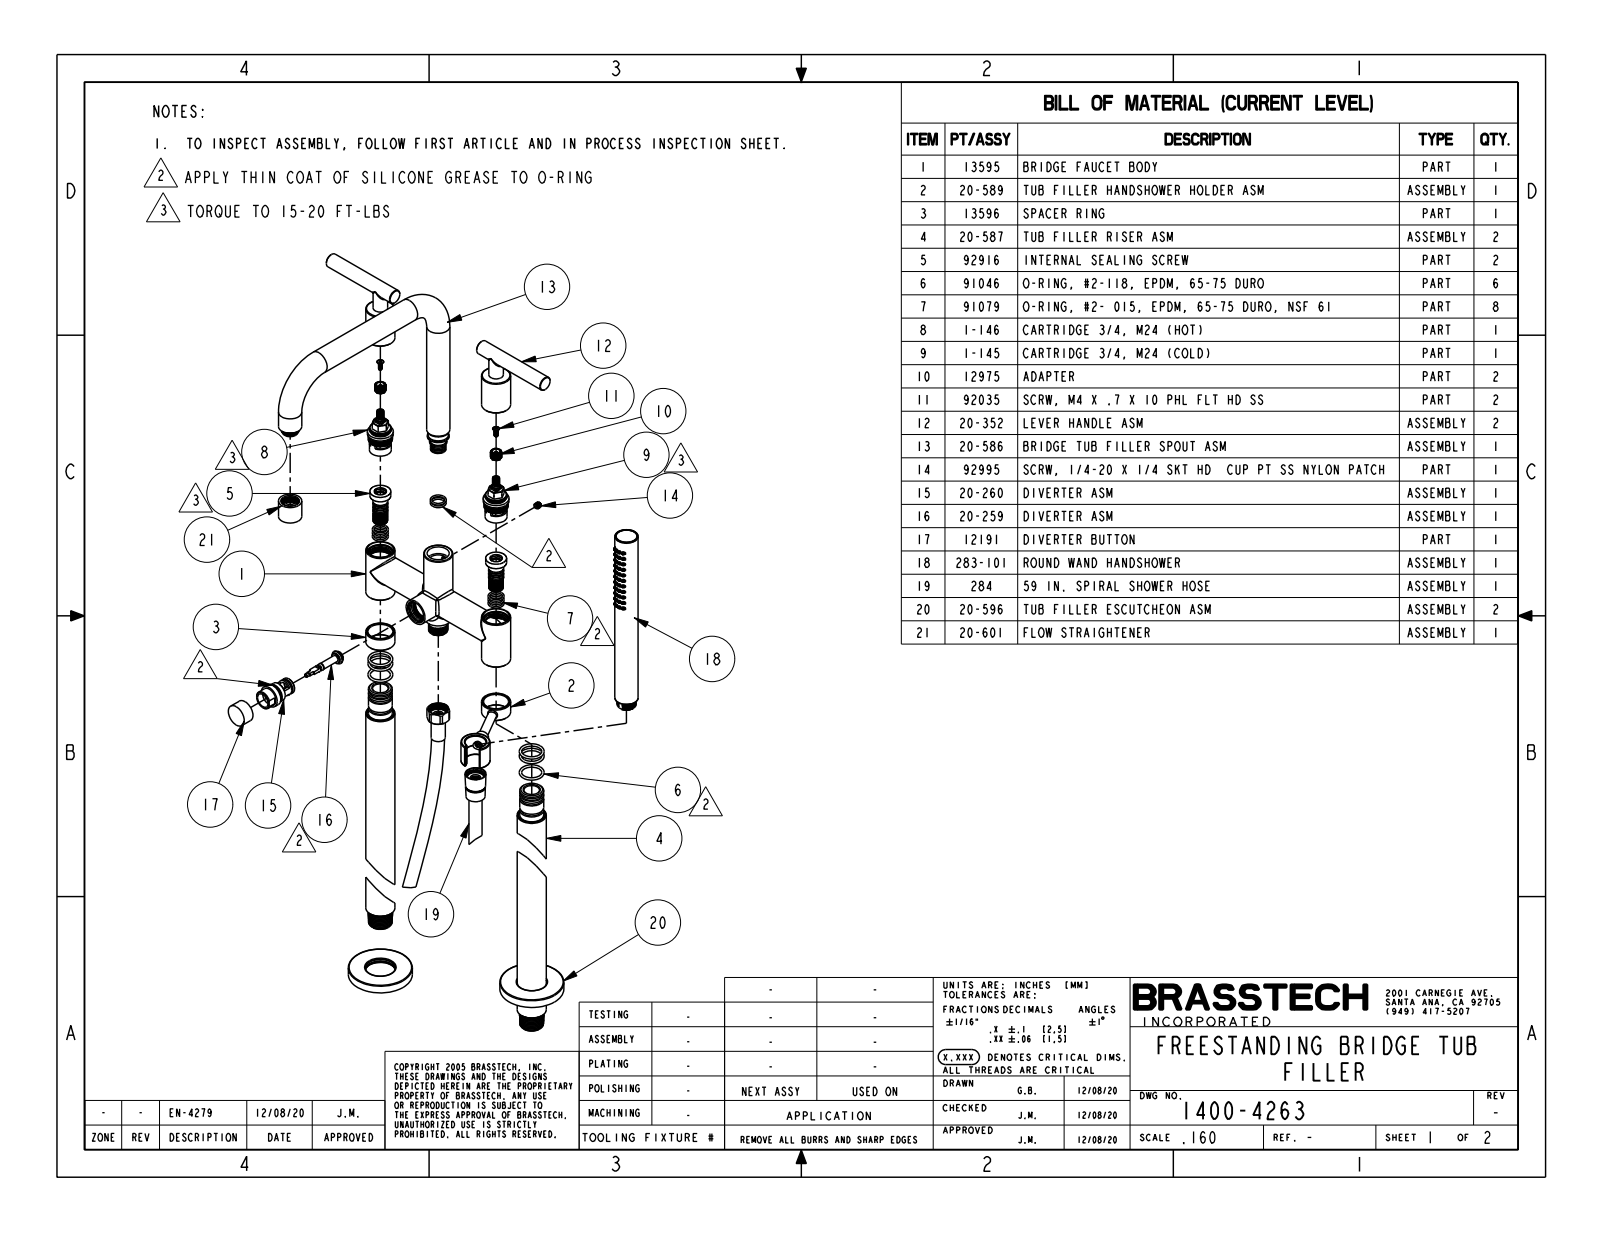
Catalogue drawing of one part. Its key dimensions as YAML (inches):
part_name: "1400-4263"
step_written_by: "CREO PARAMETRIC BY PTC INC, 2019352 (CONFIG_CONTROL_DESIGN)"
units: inches
bodies: {solids: 4, faces: 1415, planar: 212, cylindrical: 452, other: 751}
overall_size: [40.085, 15.125, 10.875]
volume: 129.3
surface_area: 514.8
round_holes:
  - {diameter: 0.14, count: 44}
  - {diameter: 0.118, count: 1}
  - {diameter: 0.606, count: 1}
  - {diameter: 0.691, count: 1}
  - {diameter: 0.94, count: 1}
round_bosses_or_shafts:
  - {diameter: 1.25, count: 5}
  - {diameter: 1, count: 4}
  - {diameter: 0.625, count: 3}
  - {diameter: 0.56, count: 3}
  - {diameter: 2.75, count: 2}
  - {diameter: 1.15, count: 2}
  - {diameter: 0.965, count: 1}
  - {diameter: 0.91, count: 1}
partial_cylinders:
  - {radius: 0.03, count: 6}
  - {radius: 0.1, count: 4}
  - {radius: 0.3, count: 1}
  - {radius: 0.34, count: 1}
  - {radius: 0.365, count: 1}
  - {radius: 0.41, count: 1}
  - {radius: 0.45, count: 1}
  - {radius: 0.494, count: 1}
face_to_face_distances: [0.38, 32.415, 32.035, 32.463, 32.083, 0.048, 2.367, 32.458, 32.078, 0.043]
hole_center_spacings: [0.604, 0.336, 0.17, 0.887, 1.172, 0.58, 0.672, 0.29]
